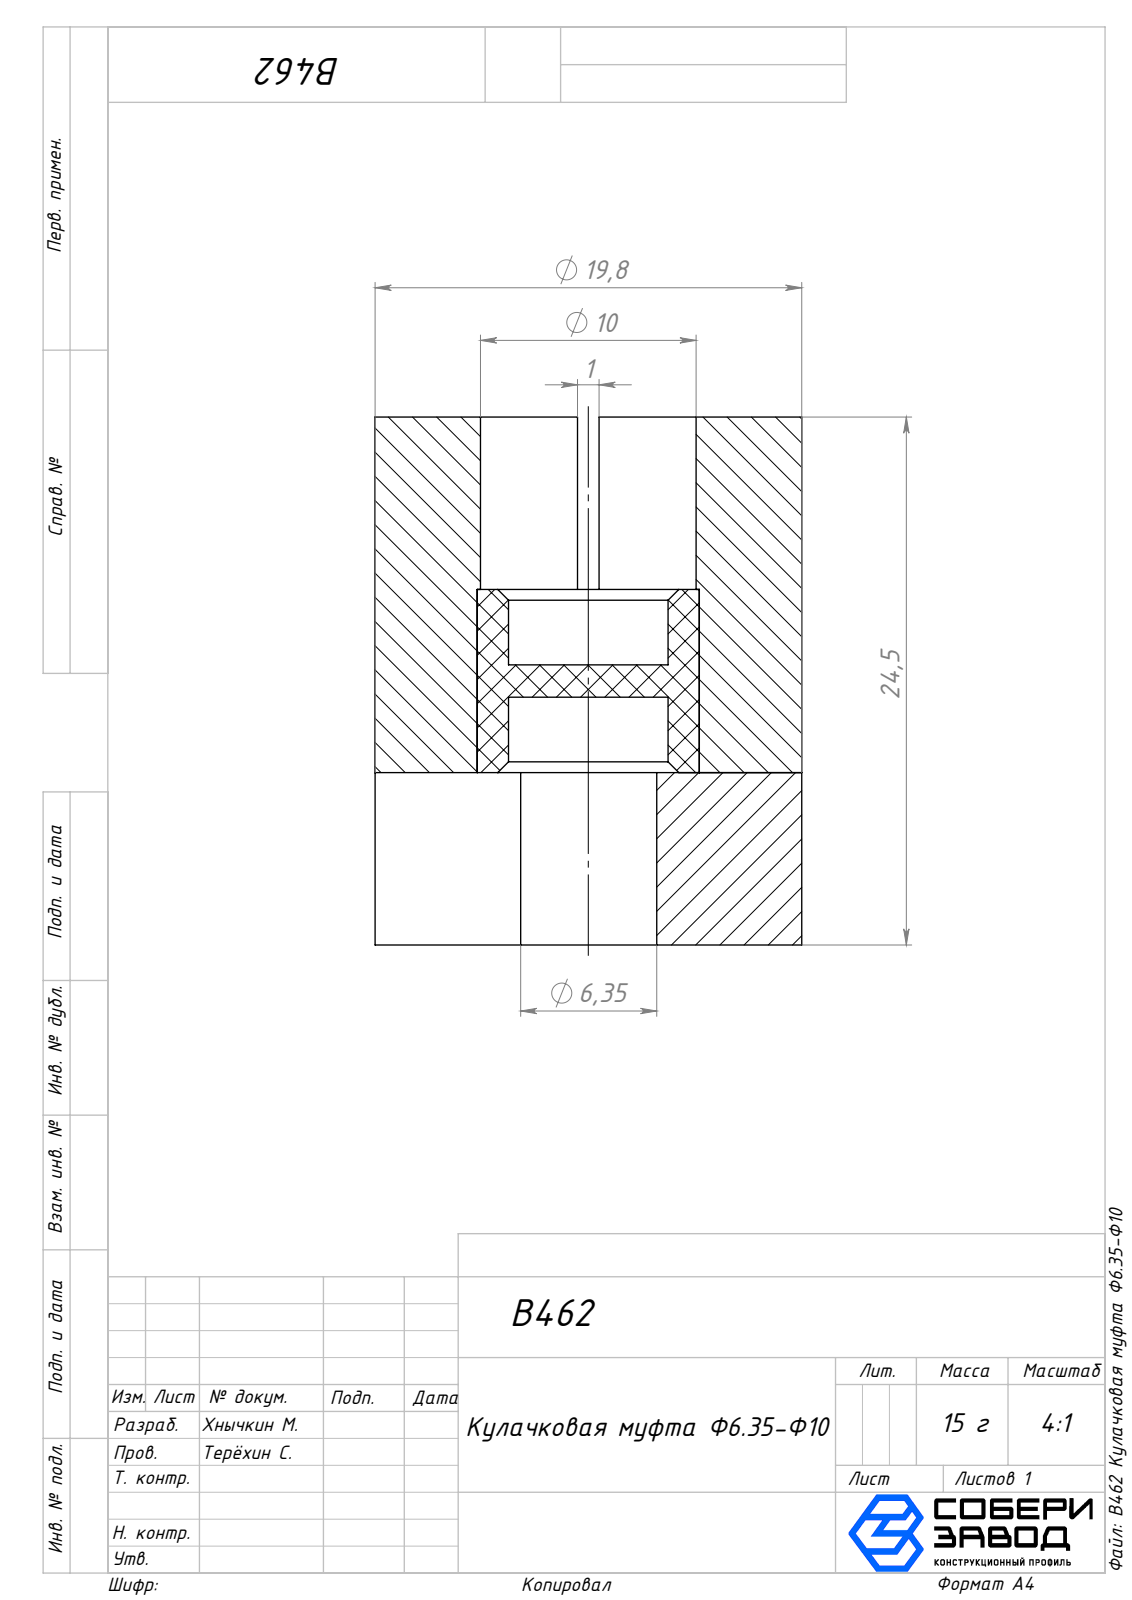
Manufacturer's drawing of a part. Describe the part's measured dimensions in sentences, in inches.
The part is named "B462 Кулачковая муфта Ф6.35-Ф10; Низ_00; Середина_00; Верх_00". Its 3-D file was written by "SolidWorks 2025 (AUTOMOTIVE_DESIGN)". It is 3 solids with 56 faces: 24 planar, 28 cylindrical and 4 other. Overall it measures 0.965 by 0.78 by 0.78 inches. Its volume is 0.382 cubic inches and its surface area 6.983 square inches. Round holes: 1 of diameter 0.25, 1 of diameter 0.291, 1 of diameter 0.394. Round bosses or shafts: 1 of diameter 0.78. Partial cylindrical surfaces (rounded edges, fillets, slot ends): 8 of radius 0.236. The main face-to-face distances are 0.315, 0.65, 0.335, 0.965, 0.183, 0.222, 0.039, 0.453, 0.512, 0.138.
